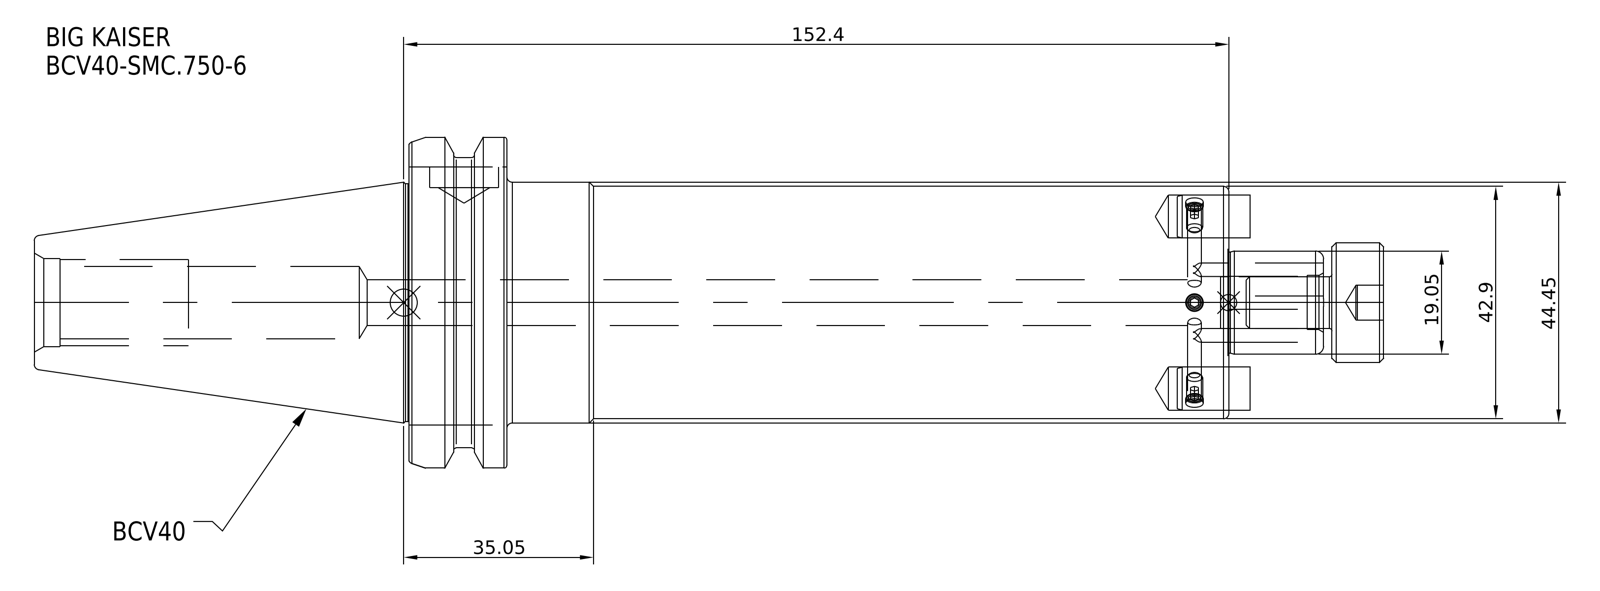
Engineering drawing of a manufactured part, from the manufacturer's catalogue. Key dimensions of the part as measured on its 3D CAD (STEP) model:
Part name (STEP PRODUCT): BCV40-SMC_750-6
STEP written by: SolidWorks 2021 (CONFIG_CONTROL_DESIGN)
Units: millimetres
Bodies: 1 solid, 38 faces (18 planar, 14 cylindrical, 6 other)
Overall size (bounding box): 224.62 × 63.5 × 63.5
Volume: 309 230 mm³ · Surface area: 38 663 mm²
Round holes (diameter × count): ⌀8.43 ×1
Round bosses / shafts (diameter × count): ⌀63.5 ×1, ⌀56.36 ×1, ⌀44.45 ×1, ⌀42.9 ×1
Main face-to-face distances: 18.05, 133.35, 151.4, 220.65, 87.3, 69.25, 117.35, 16, 34.05, 103.3
